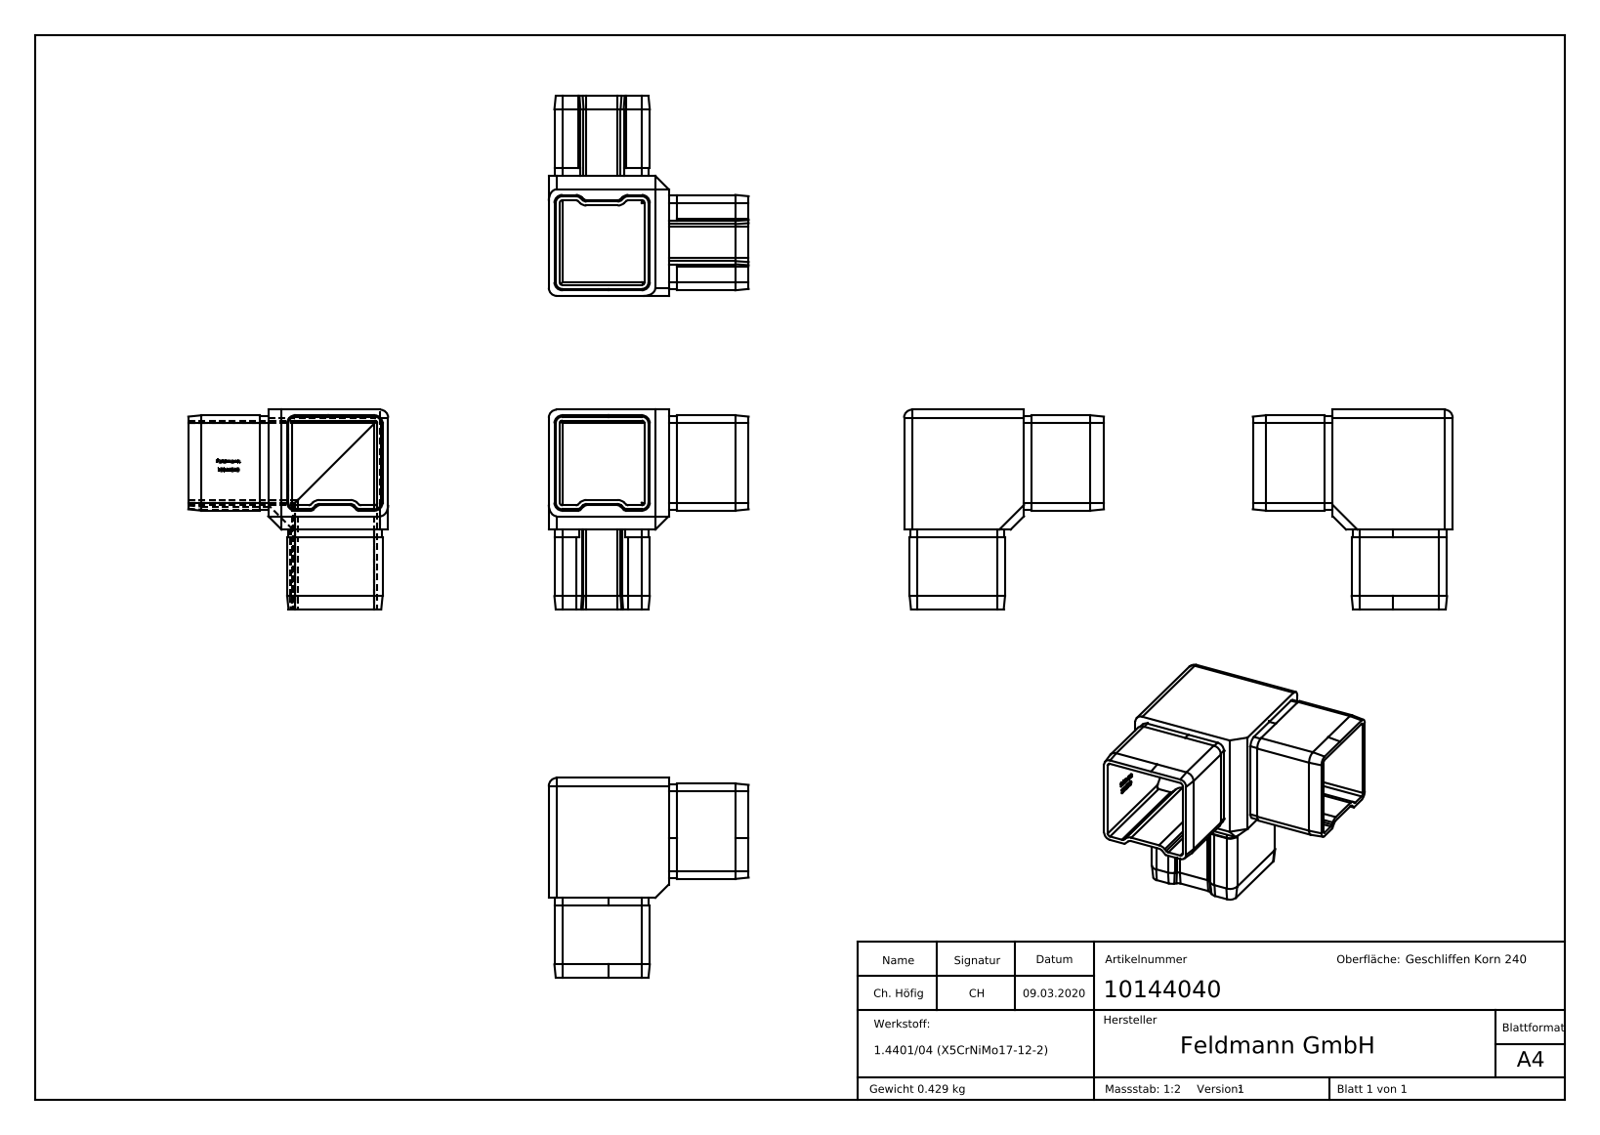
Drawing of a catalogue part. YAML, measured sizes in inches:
part_name: "10144040"
step_written_by: "SolidWorks 2015 (CONFIG_CONTROL_DESIGN)"
units: inches
bodies: {solids: 1, faces: 430, planar: 264, cylindrical: 66, other: 100}
overall_size: [2.953, 2.953, 2.953]
volume: 3.271
surface_area: 60.54
partial_cylinders:
  - {radius: 0.118, count: 17}
  - {radius: 0.039, count: 12}
  - {radius: 0.106, count: 12}
  - {radius: 0.05, count: 10}
  - {radius: 0.059, count: 6}
  - {radius: 0.138, count: 6}
  - {radius: 0.129, count: 2}
face_to_face_distances: [0.079, 1.252, 1.331, 0.161, 1.413, 0.083, 1.492, 1.409, 1.335, 1.173]
